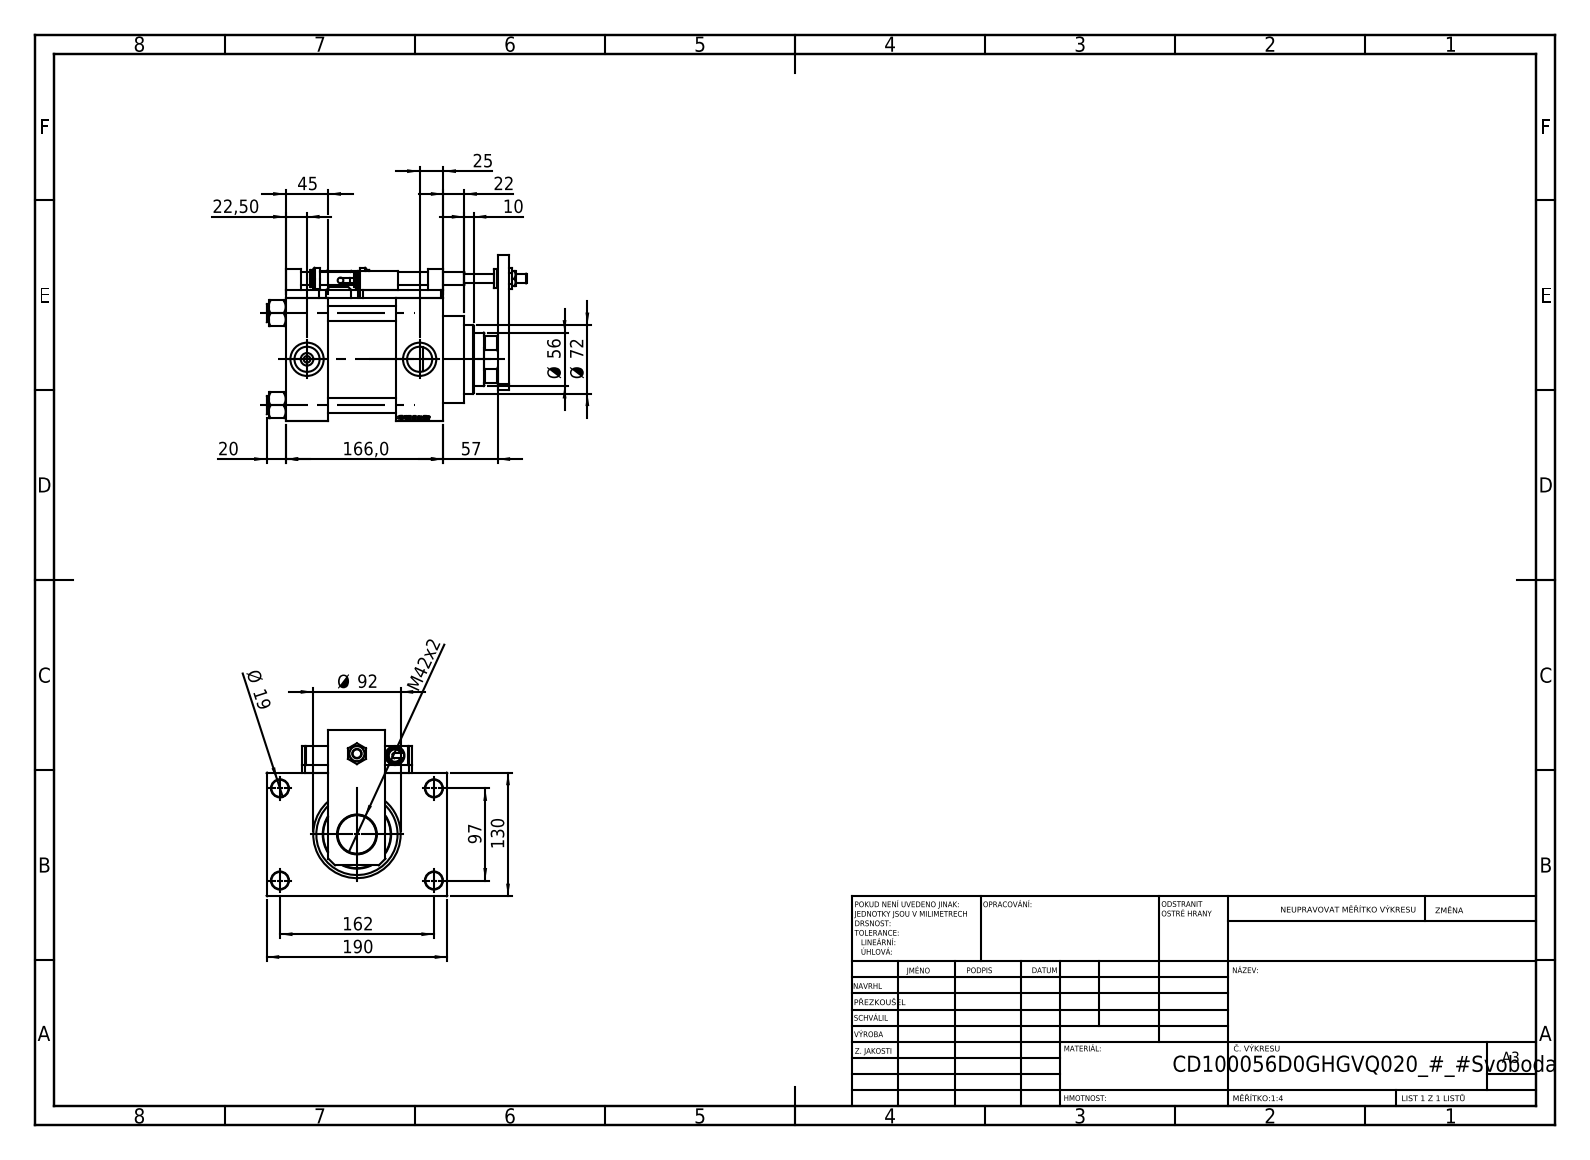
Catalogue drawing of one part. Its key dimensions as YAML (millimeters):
part_name: "V215CD_SWITCH_Q_NUT; V215CD_SWITCH_Q_TYC; V215CD_NUT_M5_D; V215CD_SWITCH_Q_NUT10 (+7 more)"
step_written_by: "SolidWorks 2019 (CONFIG_CONTROL_DESIGN)"
units: millimeters
bodies: {solids: 24, faces: 1379, planar: 666, cylindrical: 156, other: 557}
overall_size: [273.5, 190, 175]
volume: 2951000
surface_area: 458858
round_holes:
  - {diameter: 8.5, count: 4}
  - {diameter: 13.5, count: 4}
  - {diameter: 16, count: 4}
  - {diameter: 18, count: 4}
  - {diameter: 7, count: 2}
  - {diameter: 26.44, count: 2}
  - {diameter: 35, count: 2}
  - {diameter: 10, count: 1}
  - {diameter: 14, count: 1}
  - {diameter: 40.5, count: 1}
  - {diameter: 42, count: 1}
  - {diameter: 56, count: 1}
round_bosses_or_shafts:
  - {diameter: 19, count: 4}
  - {diameter: 20, count: 3}
  - {diameter: 16, count: 2}
  - {diameter: 14, count: 2}
  - {diameter: 6, count: 2}
  - {diameter: 106, count: 1}
  - {diameter: 92, count: 1}
  - {diameter: 72, count: 1}
partial_cylinders:
  - {radius: 7.5, count: 4}
  - {radius: 27, count: 1}
face_to_face_distances: [130, 45, 166, 121, 71, 8, 116, 50, 138, 190]
hole_center_spacings: [32.55, 68.52, 94.41, 96.9, 102.27, 129.45, 161.73, 32]
